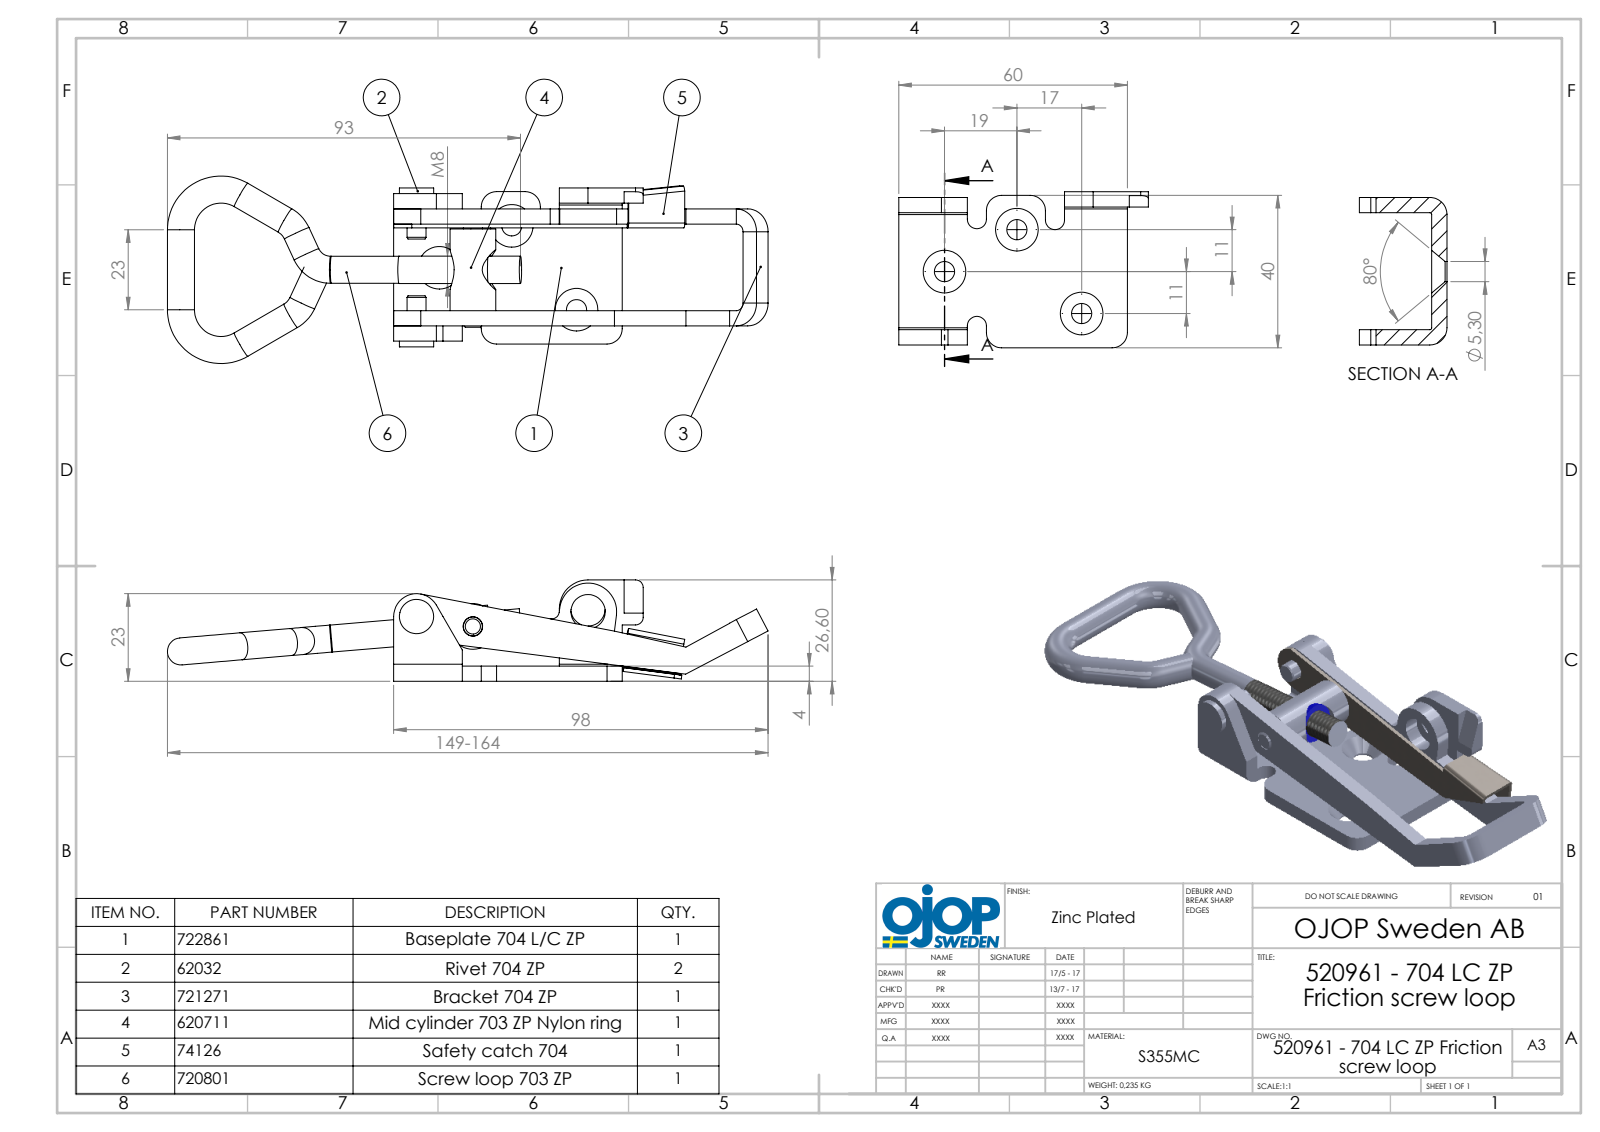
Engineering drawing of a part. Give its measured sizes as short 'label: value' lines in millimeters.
name: 704 - Rivet Gradin; 704 - Safety Catch; 703 - Skruvögla; 704 - Mount plate Safety (+5 more)
written by: SolidWorks 2015 (AUTOMOTIVE_DESIGN)
unit: mm
bodies: 8 solids, 242 faces (106 planar, 100 cylindrical, 36 other)
size: 166.31 × 49.4 × 26.6
volume: 30 068 mm³; area: 22 327 mm²
holes: 3× ⌀5.3, 2× ⌀5.1, 2× ⌀9, 1× ⌀5.4, 1× ⌀6.9, 1× ⌀7.2, 1× ⌀7.7, 1× ⌀10.5
bosses: 4× ⌀7, 2× ⌀5, 1× ⌀12, 1× ⌀9, 1× ⌀7.7
rounds: 5× R2, 4× R4, 3× R0.3, 3× R0.5, 3× R1.3, 3× R2.5, 3× R4.5, 3× R6
face distances: 4, 26.7, 30.7, 1, 22.7, 5.5, 32.2, 36.2, 5, 21.7
hole spacings: 0.74, 15.02, 21.95, 27.8, 30.49, 30.56, 37.64, 45.04
